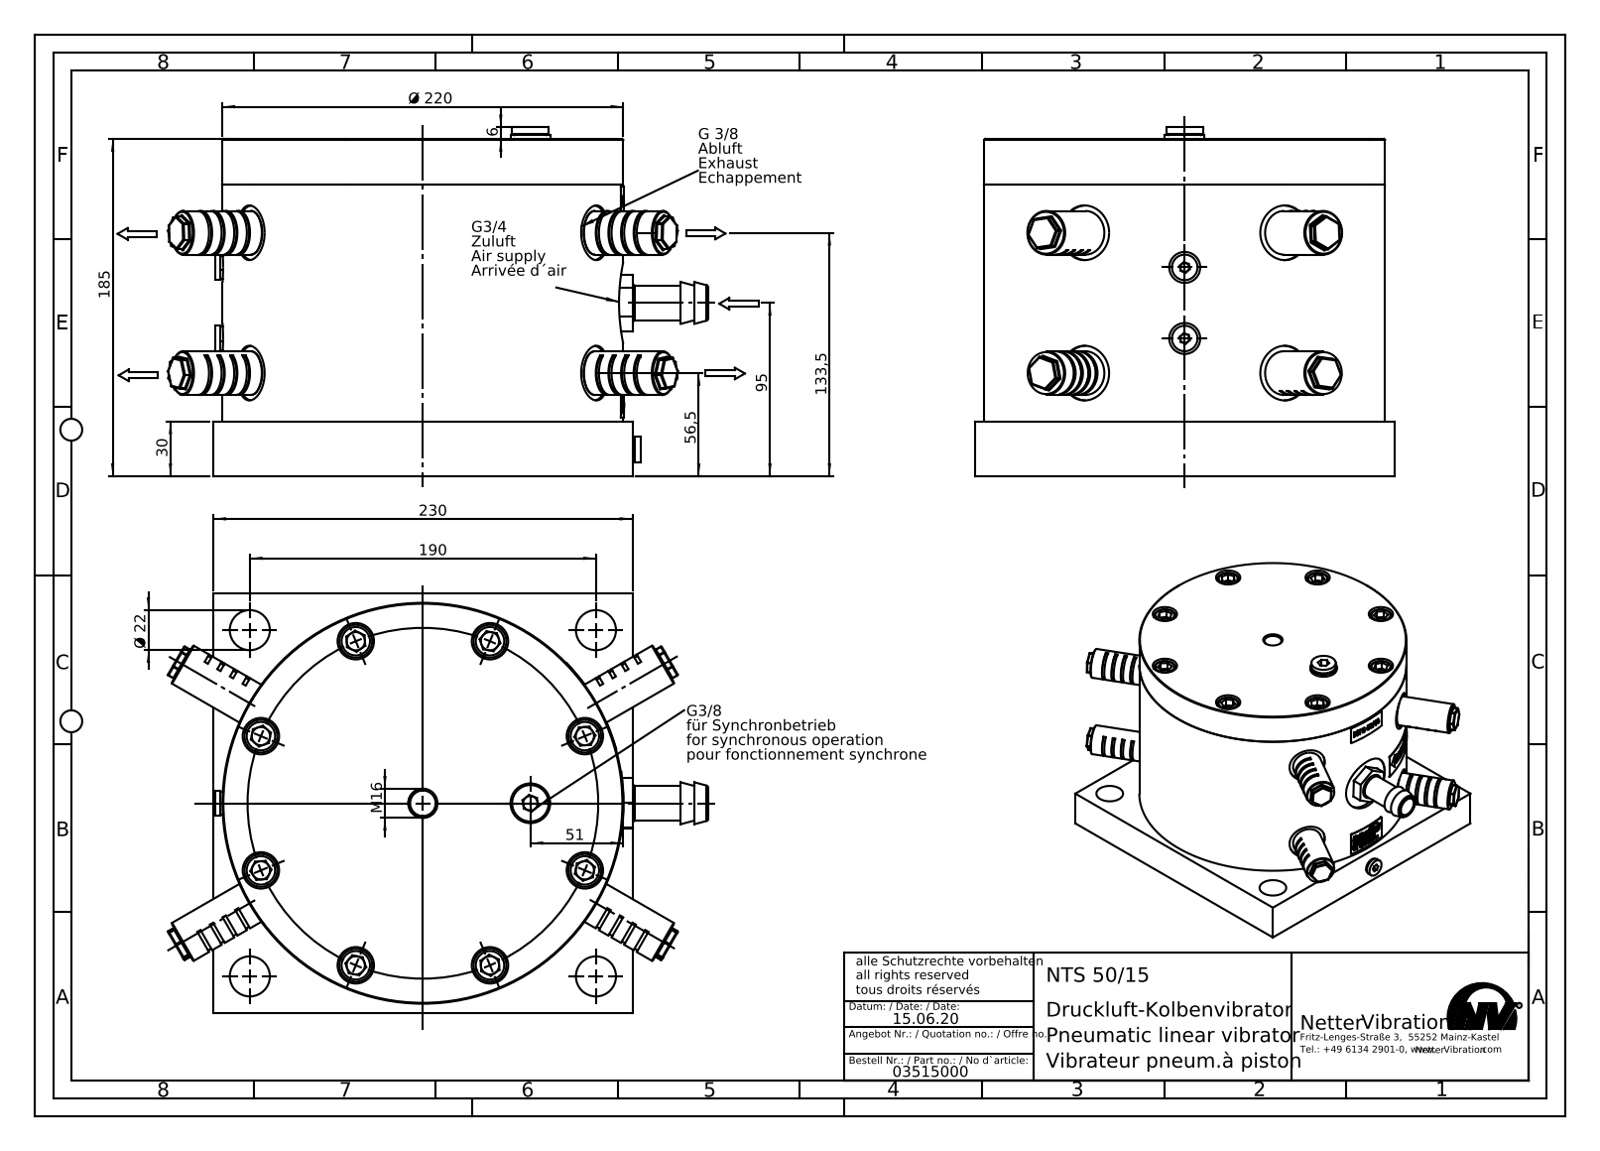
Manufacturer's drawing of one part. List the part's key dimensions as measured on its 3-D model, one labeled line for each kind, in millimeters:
Part name (STEP PRODUCT): NTS 50-15 Kolbenvibrator #03515000
STEP written by: SolidWorks 2015 (AUTOMOTIVE_DESIGN)
Units: millimetres
Bodies: 40 solids, 1700 faces (573 planar, 713 cylindrical, 414 other)
Overall size (bounding box): 298.4 × 230 × 191.36
Volume: 7 519 000 mm³ · Surface area: 544 944 mm²
Round holes (diameter × count): ⌀10.2 ×8, ⌀12.5 ×8, ⌀20 ×8, ⌀14.95 ×5, ⌀22 ×4, ⌀30 ×4, ⌀6 ×3, ⌀8.57 ×3, ⌀10 ×3, ⌀17 ×3, ⌀2 ×2, ⌀3 ×1
Round bosses / shafts (diameter × count): ⌀24 ×8, ⌀18 ×8, ⌀12 ×8, ⌀16.66 ×4, ⌀14 ×3, ⌀13 ×3, ⌀9.73 ×3, ⌀220 ×1
Partial cylindrical surfaces — rounded edges, fillets, slot ends (radius × count): R0.5 ×156, R11 ×8, R110.2 ×1
Main face-to-face distances: 130, 155, 25, 30, 160, 185, 159, 1, 184, 29
Hole centre spacings: 58.49, 96.25, 131.97, 136.11, 177.84, 192.9, 226.29, 73.66
